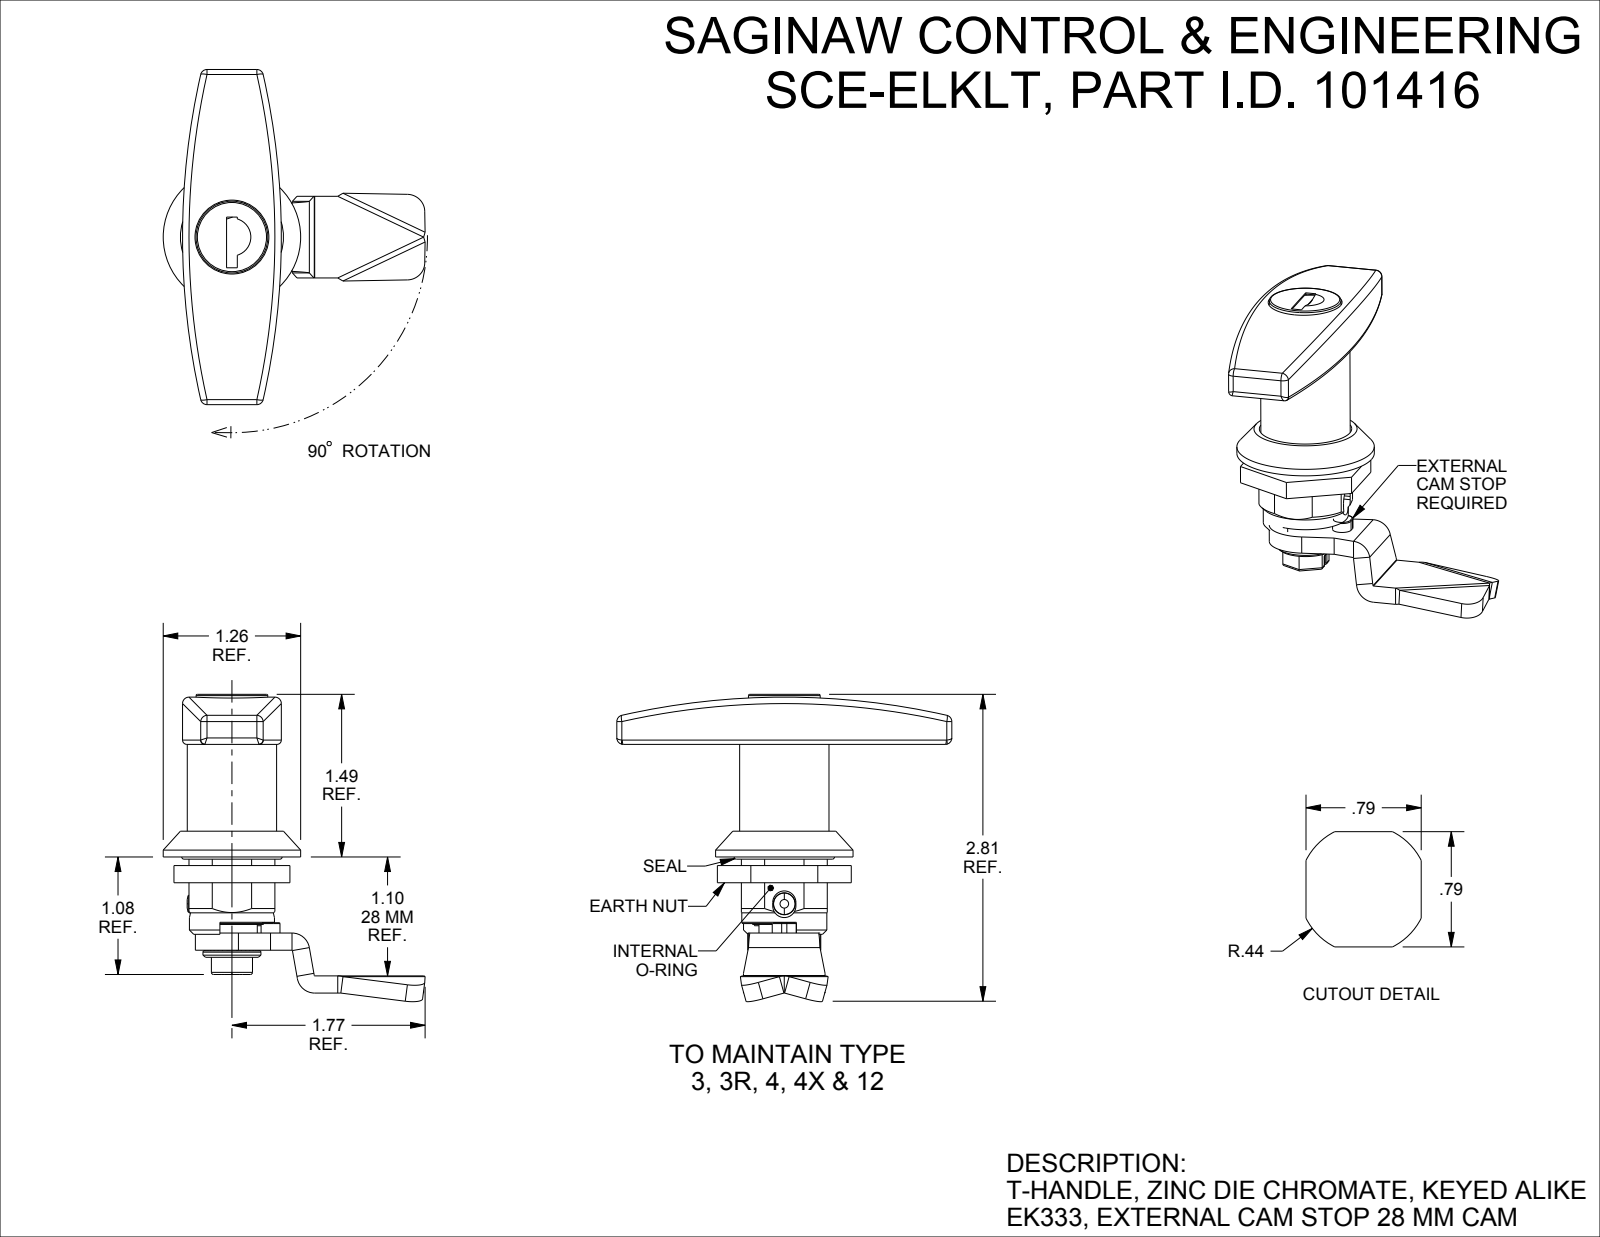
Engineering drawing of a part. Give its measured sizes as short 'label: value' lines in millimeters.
name: SCE-ELKLT
written by: SolidWorks 2021 (AUTOMOTIVE_DESIGN)
unit: mm
bodies: 10 solids, 596 faces (335 planar, 165 cylindrical, 96 other)
size: 78 × 71.5 × 61
volume: 28 500 mm³; area: 23 390 mm²
holes: 2× ⌀5.1, 1× ⌀2.6, 1× ⌀8, 1× ⌀8.7, 1× ⌀12, 1× ⌀15, 1× ⌀16.1, 1× ⌀17.2, 1× ⌀20.3, 1× ⌀21.5
bosses: 1× ⌀32, 1× ⌀20.8, 1× ⌀19.8, 1× ⌀16.7, 1× ⌀14.8, 1× ⌀13.5, 1× ⌀12, 1× ⌀11.8
rounds: 30× R0.3, 18× R0.5, 8× R1.5, 4× R4, 3× R171.2, 2× R0.1, 2× R0.2, 2× R2.2
face distances: 4, 2, 15.7, 25.7, 10, 29.7, 19.7, 6, 21.7, 20
hole spacings: 11
